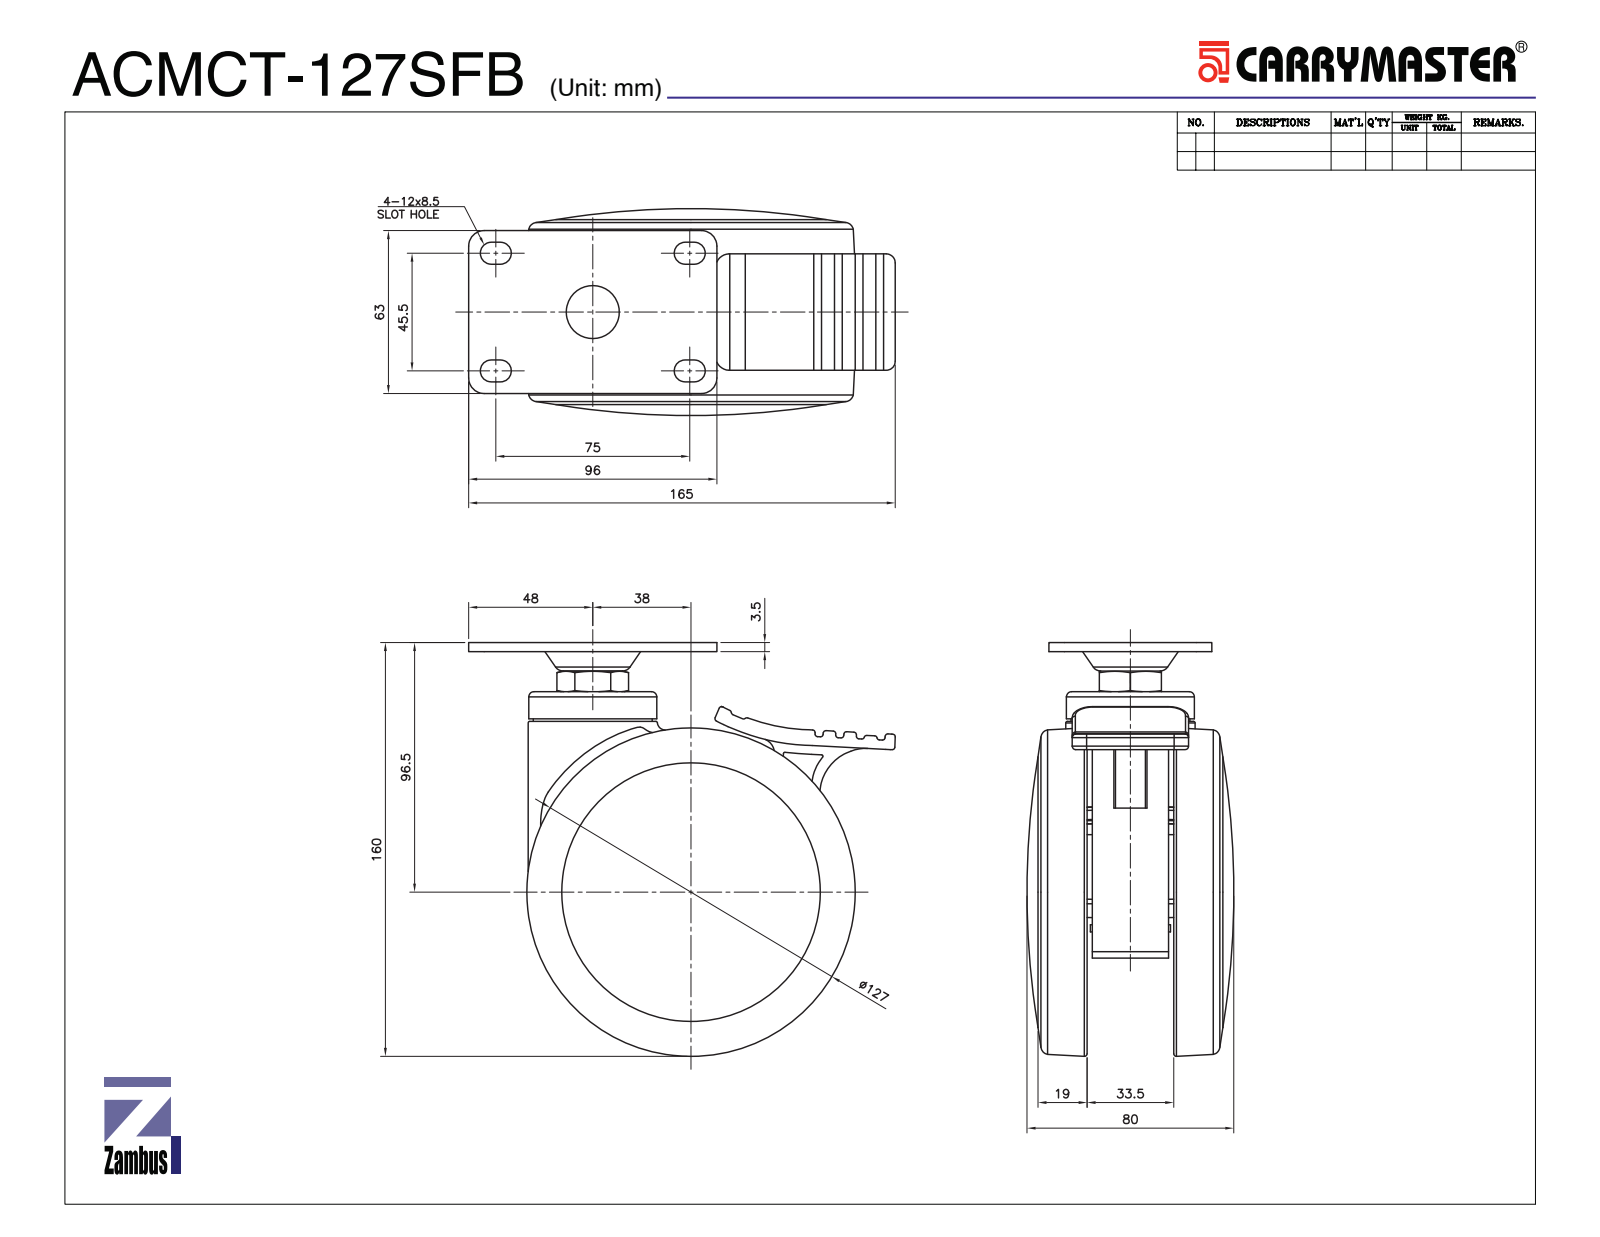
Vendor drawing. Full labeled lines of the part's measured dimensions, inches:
Part name (STEP PRODUCT): TOP PLATE; 127 BRAKE TYPE FRAME; WHEEL; BOLT-1 (+2 more)
STEP written by: SolidWorks 2019 (CONFIG_CONTROL_DESIGN)
Units: inches
Bodies: 6 solids, 515 faces (144 planar, 250 cylindrical, 121 other)
Overall size (bounding box): 6.496 × 6.299 × 3.149
Volume: 43.68 in³ · Surface area: 215.3 in²
Round holes (diameter × count): ⌀1.181 ×1, ⌀3.661 ×1, ⌀3.945 ×1
Round bosses / shafts (diameter × count): ⌀3.937 ×1, ⌀1.969 ×1, ⌀1.811 ×1, ⌀1.772 ×1, ⌀0.787 ×1, ⌀0.669 ×1, ⌀0.63 ×1, ⌀0.472 ×1
Partial cylindrical surfaces — rounded edges, fillets, slot ends (radius × count): R0.02 ×58, R0.039 ×42, R0.167 ×8, R0.197 ×6, R0.118 ×4, R0.236 ×4, R0.394 ×2, R3.937 ×2
Main face-to-face distances: 0.472, 0.394, 0.079, 1.634, 1.713, 1.24, 1.161, 2.106, 1.319, 0.138
